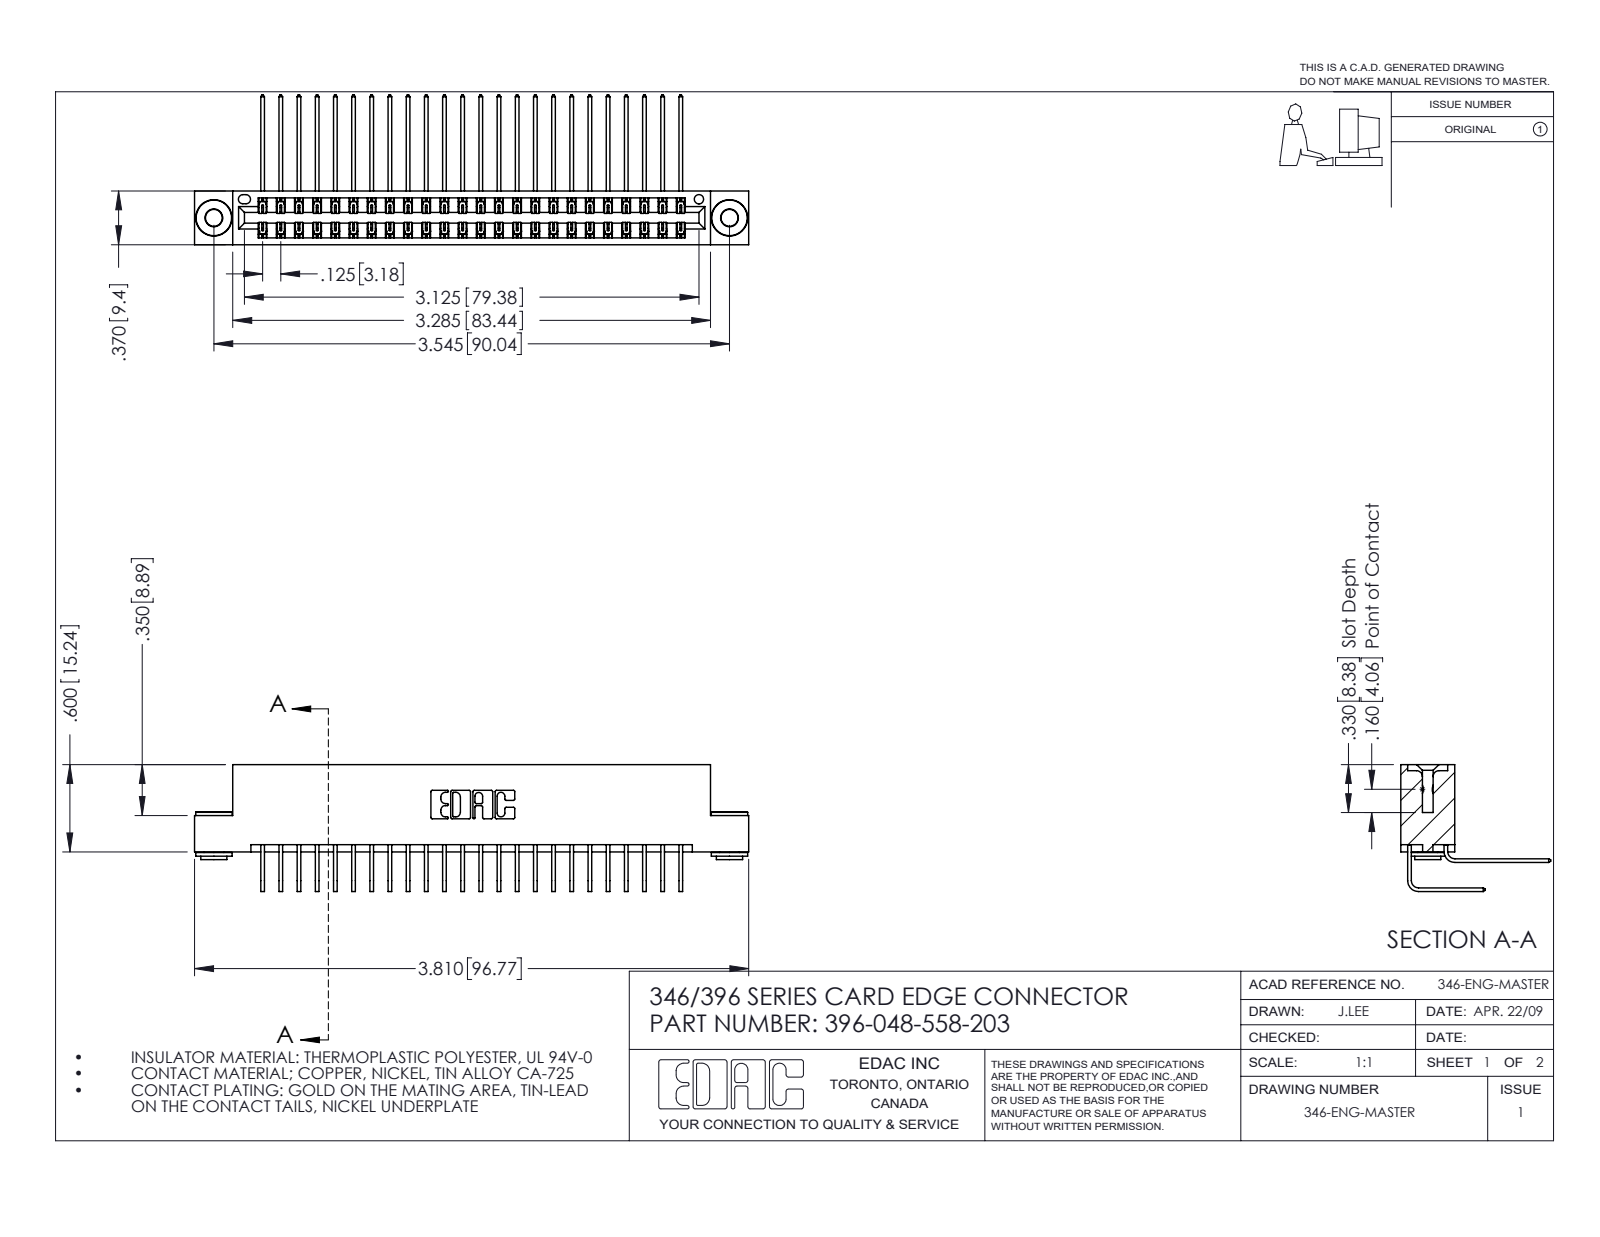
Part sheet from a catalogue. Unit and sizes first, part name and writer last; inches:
Units: inches
Overall size (bounding box): 3.81 × 1.03 × 0.873
Round holes (diameter × count): ⌀0.116 ×2, ⌀0.156 ×2, ⌀0.064 ×1
Round bosses / shafts (diameter × count): ⌀0.25 ×2, ⌀0.18 ×2, ⌀0.136 ×2
Partial cylindrical surfaces — rounded edges, fillets, slot ends (radius × count): R0.006 ×72, R0.01 ×22, R0.007 ×6, R0.031 ×6, R0.026 ×3, R0.014 ×2, R0.022 ×2, R0.024 ×2
Main face-to-face distances: 0.322, 0.048, 0.25, 0.025, 0.37, 0.298, 0.072, 0.275, 0.148, 0.222
Hole centre spacings: 0.246, 3.337, 3.545
Volume: 0.585 in³ · Surface area: 22.39 in²
Bodies: 51 solids, 2752 faces (1862 planar, 882 cylindrical, 8 other)
Part name (STEP PRODUCT): 345-292-001_558 559 Tail - 1; 345-250-002_345-250-002-102; 396-048-558-203; 346 Part_Flush Mounting Lugs - 0.156 Dia-TH (+1 more)
STEP written by: SolidWorks 2016 (CONFIG_CONTROL_DESIGN)
